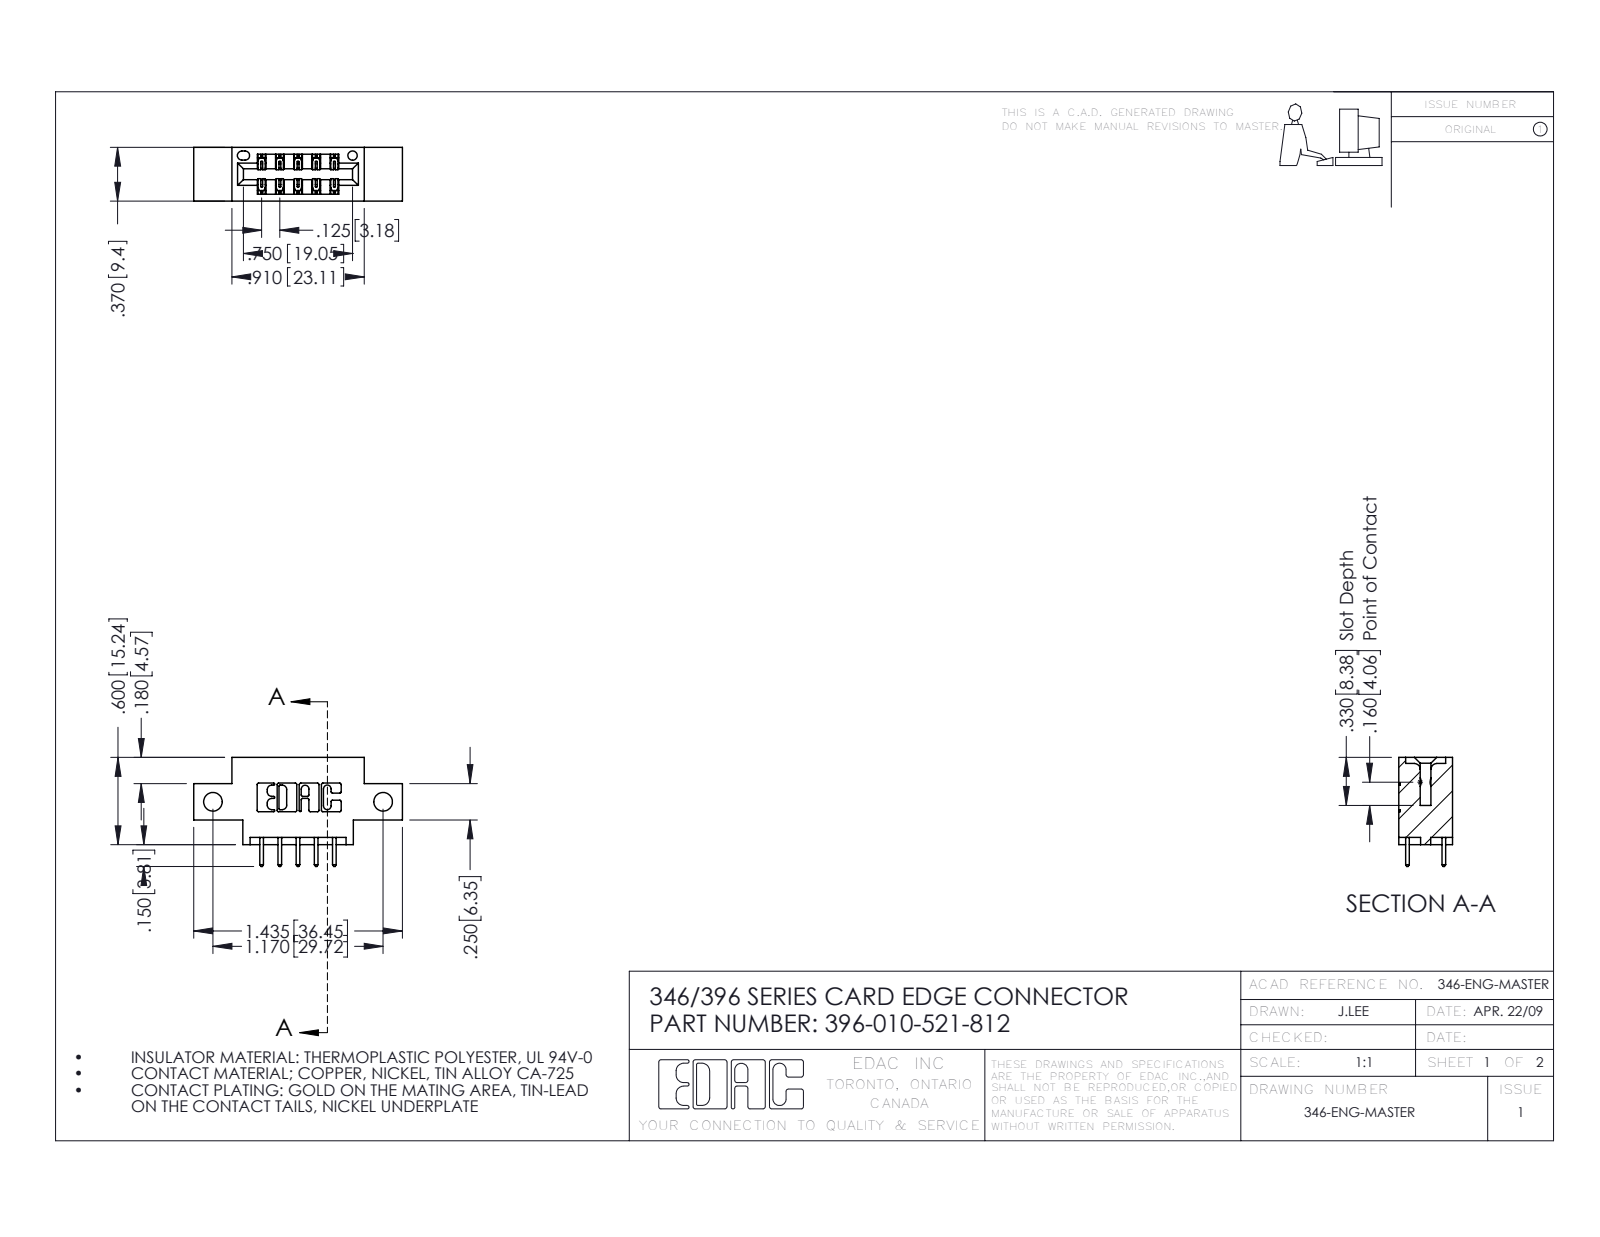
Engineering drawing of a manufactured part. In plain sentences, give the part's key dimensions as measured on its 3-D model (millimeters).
The part is named "396-010-521-812; 345-292-001_345-293-121; 346 Part_0.170 Offset - Side Mount". Its 3-D file was written by "SolidWorks 2016 (CONFIG_CONTROL_DESIGN)". It is 11 solids with 646 faces: 430 planar, 216 cylindrical and 0 other. Overall it measures 36.4 by 19.1 by 9.4 millimeters. Its volume is 3 020 cubic millimeters and its surface area 3 586 square millimeters. Round holes: 2 of diameter 3.3, 1 of diameter 1.6. Partial cylindrical surfaces (rounded edges, fillets, slot ends): 22 of radius 0.3, 15 of radius 0.2, 10 of radius 0.3, 6 of radius 0.2, 6 of radius 0.8, 3 of radius 0.7, 2 of radius 0.4, 2 of radius 0.6. The main face-to-face distances are 6.4, 9.4, 1.2, 8.2, 1.8, 7.6, 0.6, 3.8, 5.6, 2.5. The hole center spacings are 29.7.
